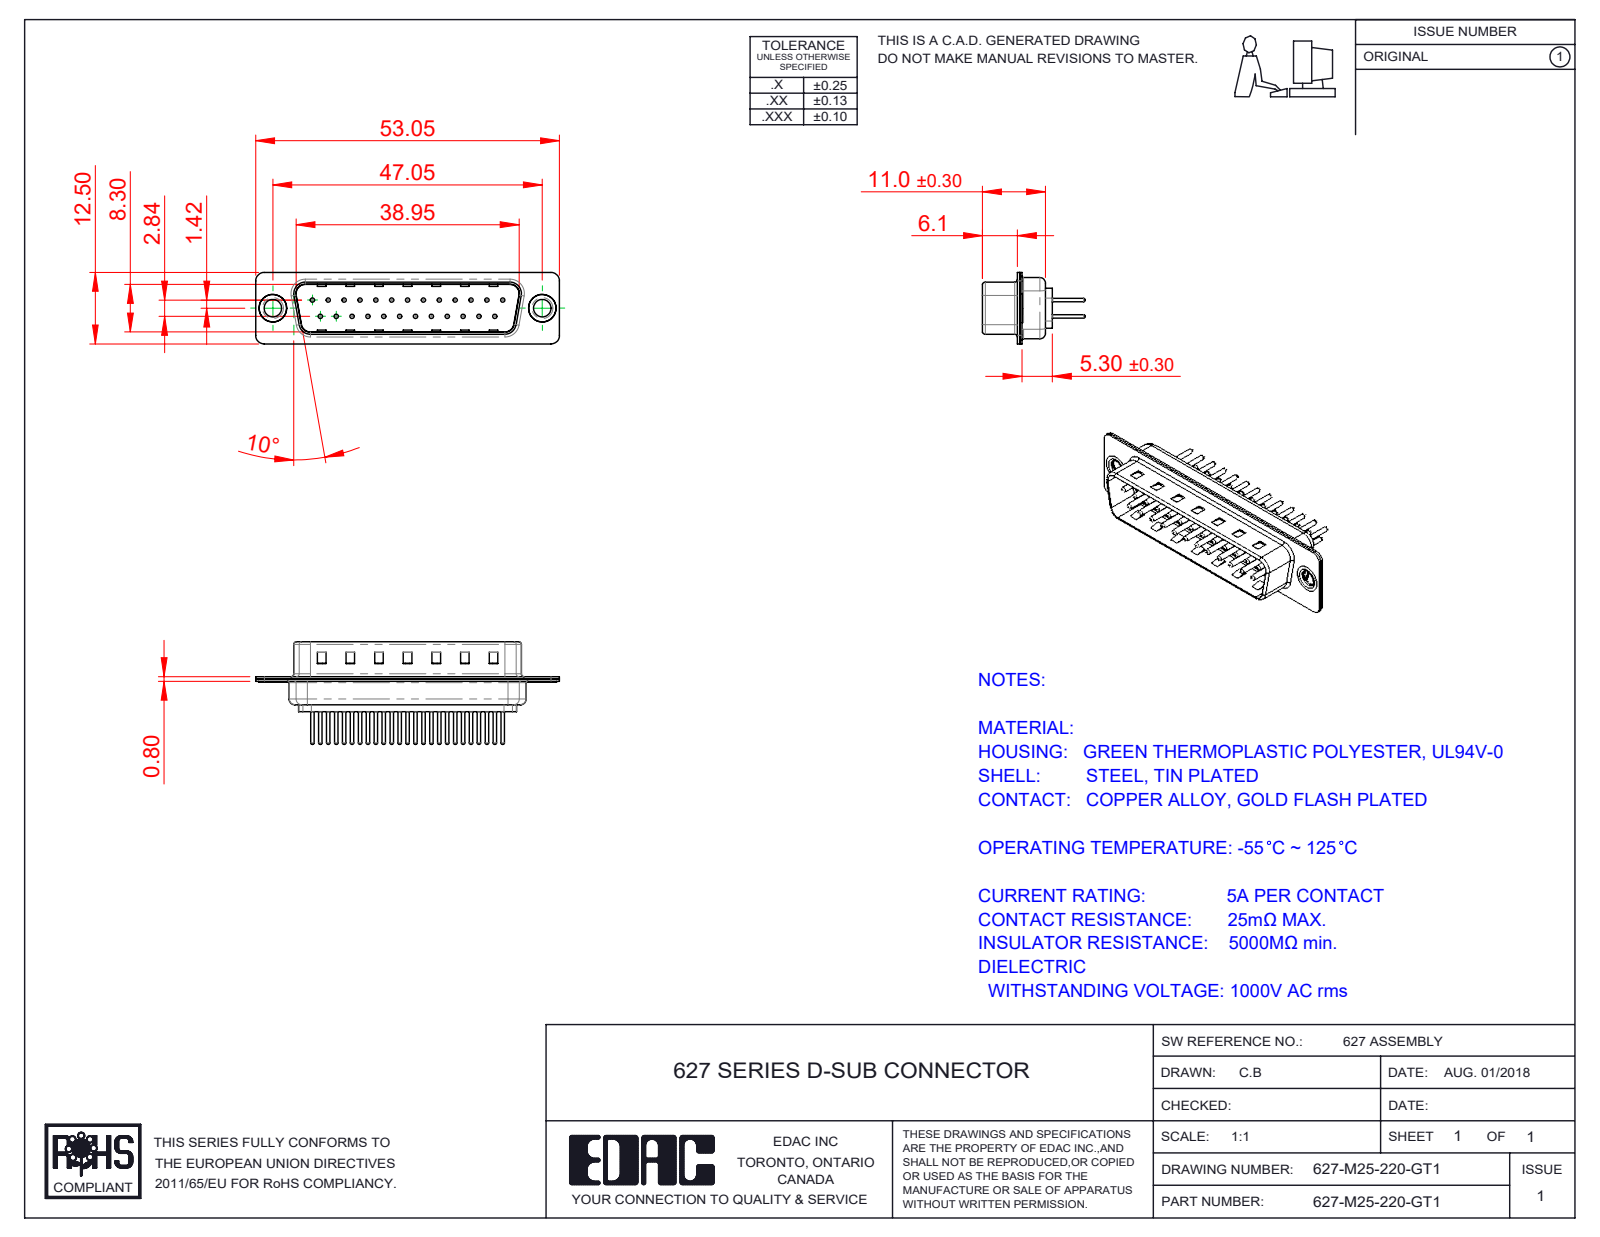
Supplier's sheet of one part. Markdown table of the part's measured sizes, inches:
| quantity | value |
| --- | --- |
| part name | 627M Housing_25 Contacts; 627M Shell Front_25 Contacts; 627M Shell Rear_25 Contacts; 627M Thru Hole Rivet (+3 more) |
| STEP written by | SolidWorks 2020 (CONFIG_CONTROL_DESIGN) |
| units | inches |
| bodies | 30 solids, 1275 faces (346 planar, 471 cylindrical, 458 other) |
| overall size | 2.089 × 0.705 × 0.492 |
| volume | 0.161 in³ |
| surface area | 10.38 in² |
| round holes (diameter × count) | 0.03 × 25, 0.063 × 25, 0.079 × 25, 0.12 × 2, 0.157 × 2, 0.189 × 2 |
| round bosses / shafts (diameter × count) | 0.059 × 25, 0.024 × 25, 0.197 × 2, 0.193 × 2, 0.14 × 2 |
| partial cylindrical surfaces (radius × count) | 0.059 × 16, 0.079 × 12, 0.02 × 8, 0.063 × 8, 0.01 × 4, 0.024 × 4, 0.026 × 4, 0.035 × 4 |
| main face-to-face distances | 0.016, 0.031, 0.374, 0.358, 0.343, 0.39, 0.047, 0.24, 0.224, 0.03 |
| hole center spacings | 0.124, 0.109, 0.218, 0.327, 0.436, 0.545, 0.654, 0.198 |
